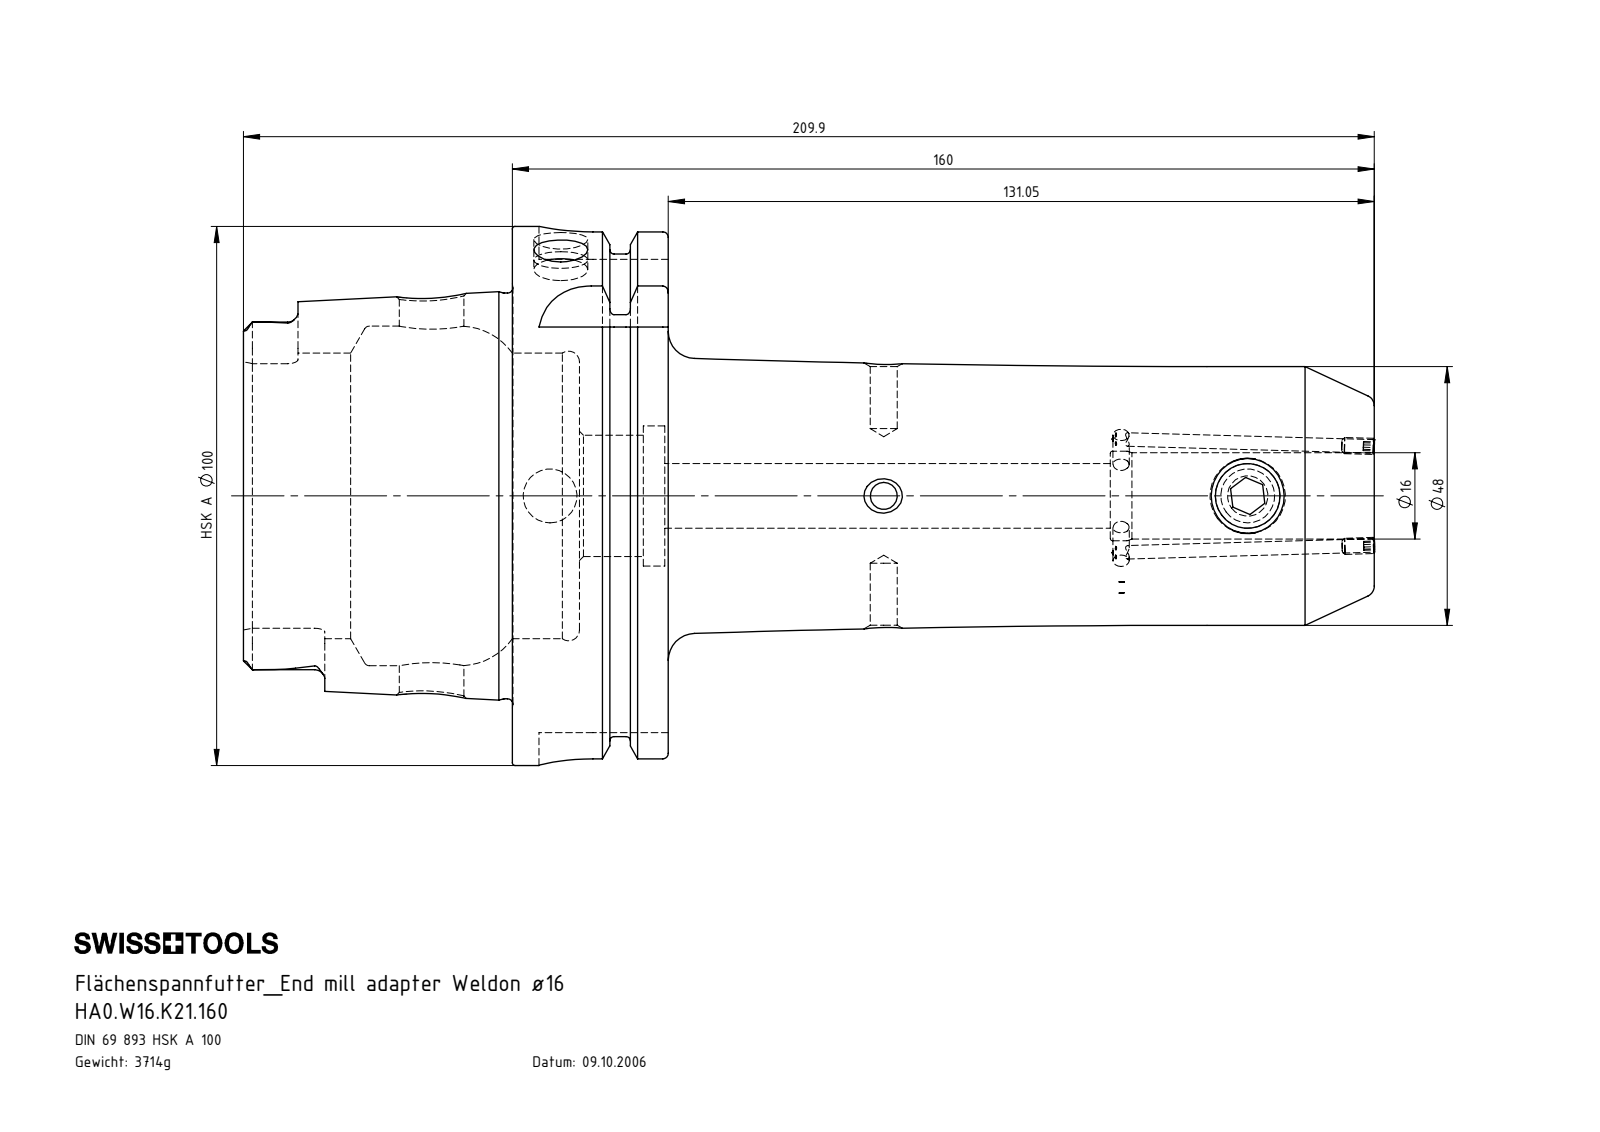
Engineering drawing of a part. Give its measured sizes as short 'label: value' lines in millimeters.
name: HA0.W16.K21.160; ERU-CJ2.001.006_Default; W16-ER1.001.016_Default; HA0-W16.K21.160_C_Fertigbearbeitung
written by: SolidWorks 2009 (CONFIG_CONTROL_DESIGN)
unit: mm
bodies: 4 solids, 278 faces (73 planar, 85 cylindrical, 120 other)
size: 209.98 × 100 × 100
volume: 473 153 mm³; area: 77 243 mm²
holes: 3× ⌀10, 3× ⌀12, 2× ⌀2.5, 2× ⌀5, 1× ⌀3, 1× ⌀16, 1× ⌀16.6, 1× ⌀22.5, 1× ⌀26, 1× ⌀53, 1× ⌀63
bosses: 2× ⌀3, 1× ⌀100, 1× ⌀91.95, 1× ⌀75.26, 1× ⌀48, 1× ⌀14
rounds: 6× R1.9, 4× R4.88, 4× R10
face distances: 28.95, 16.5, 12.45, 49.9, 62.35, 78.85, 209.9, 160, 147.55, 131.05
hole spacings: 61.95, 67.55, 83.95, 129.5
